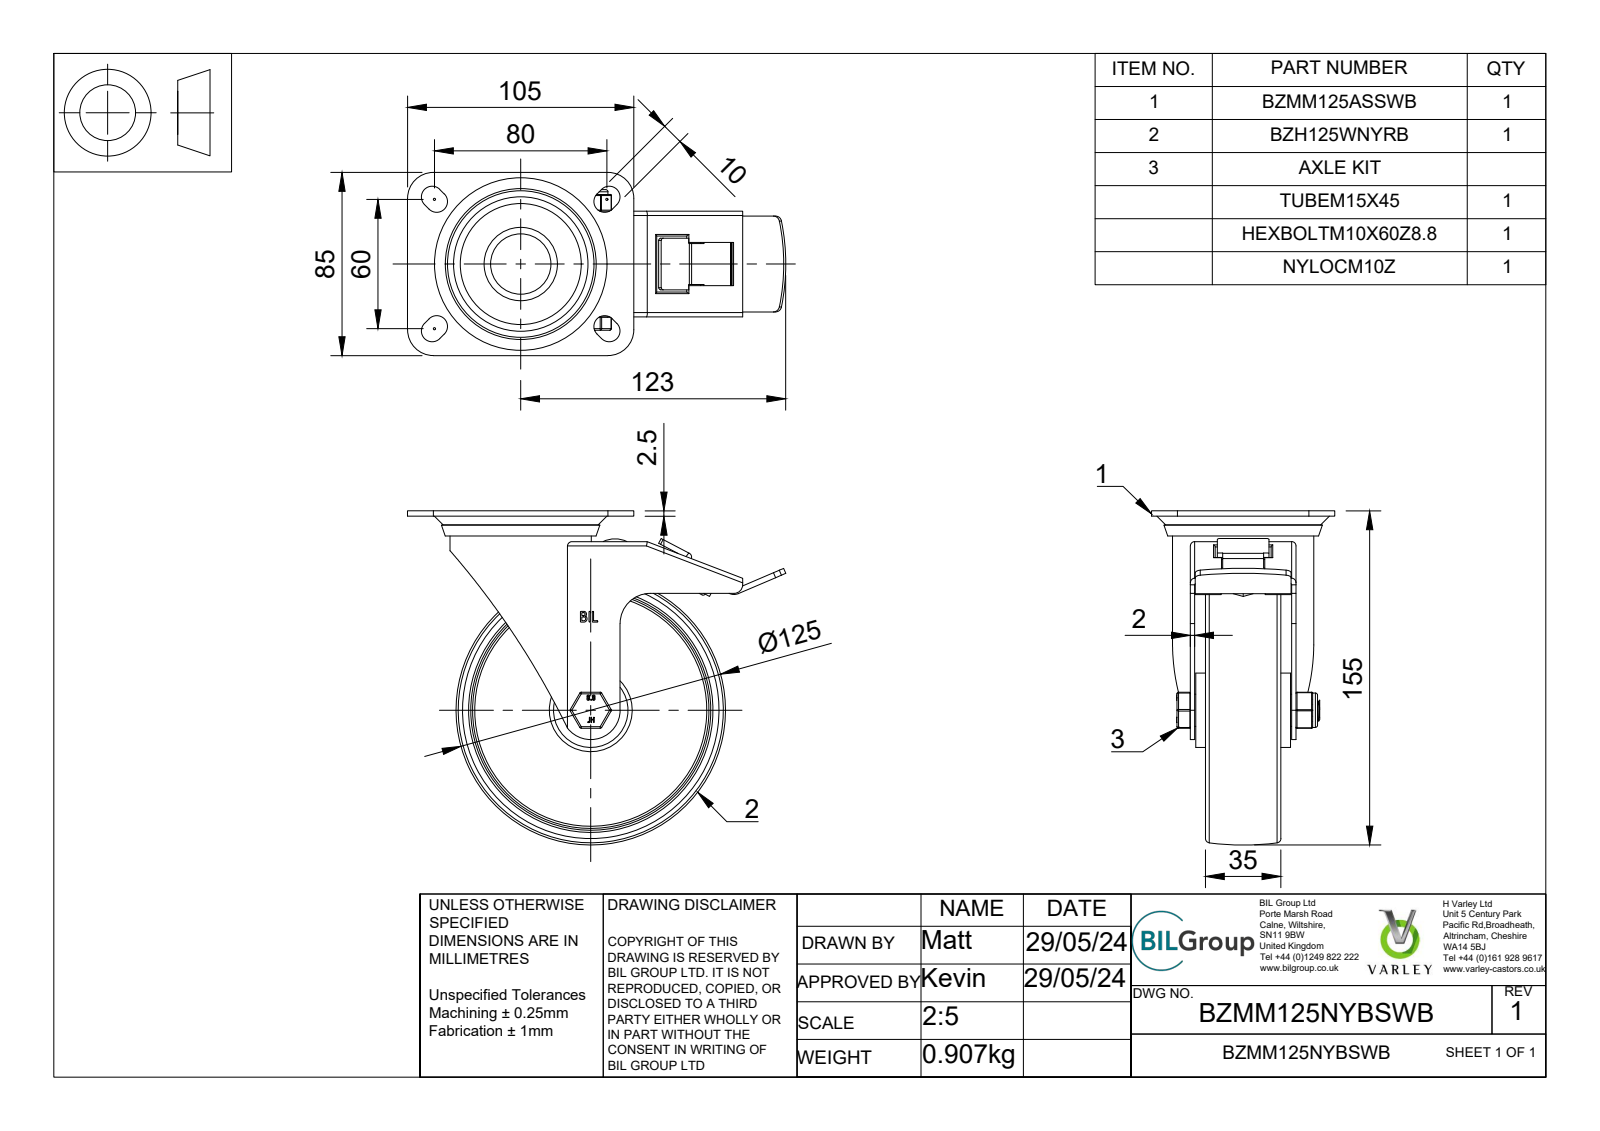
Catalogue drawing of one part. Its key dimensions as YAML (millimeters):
part_name: "BZMM125NYBSWB v3; BZMM125ASSWB v1; ZINC PLATED, PRESSED STEEL TOP PLATE; ZINC PLATED, PRESSED STEEL FORKS (+8 more)"
step_written_by: "Autodesk Translation Framework v13.14.0.145 (AUTOMOTIVE_DESIGN)"
units: millimeters
bodies: {solids: 24, faces: 715, planar: 385, cylindrical: 229, other: 101}
overall_size: [175.5, 155, 85]
volume: 292941
surface_area: 145470
round_holes:
  - {diameter: 6, count: 2}
  - {diameter: 10, count: 1}
  - {diameter: 10.2, count: 1}
  - {diameter: 12, count: 1}
  - {diameter: 15, count: 1}
  - {diameter: 28, count: 1}
  - {diameter: 40, count: 1}
  - {diameter: 61.5, count: 1}
round_bosses_or_shafts:
  - {diameter: 4, count: 8}
  - {diameter: 65.5, count: 1}
  - {diameter: 34.5, count: 1}
  - {diameter: 34, count: 1}
  - {diameter: 23, count: 1}
  - {diameter: 22.75, count: 1}
  - {diameter: 16, count: 1}
  - {diameter: 15.5, count: 1}
partial_cylinders:
  - {radius: 0.5, count: 18}
  - {radius: 0.75, count: 16}
  - {radius: 1.5, count: 12}
  - {radius: 5, count: 9}
  - {radius: 1, count: 8}
  - {radius: 2, count: 6}
  - {radius: 3, count: 4}
  - {radius: 12, count: 4}
face_to_face_distances: [2, 9, 2.5, 5, 29, 20, 18, 47, 7, 27]
hole_center_spacings: [43.75]
